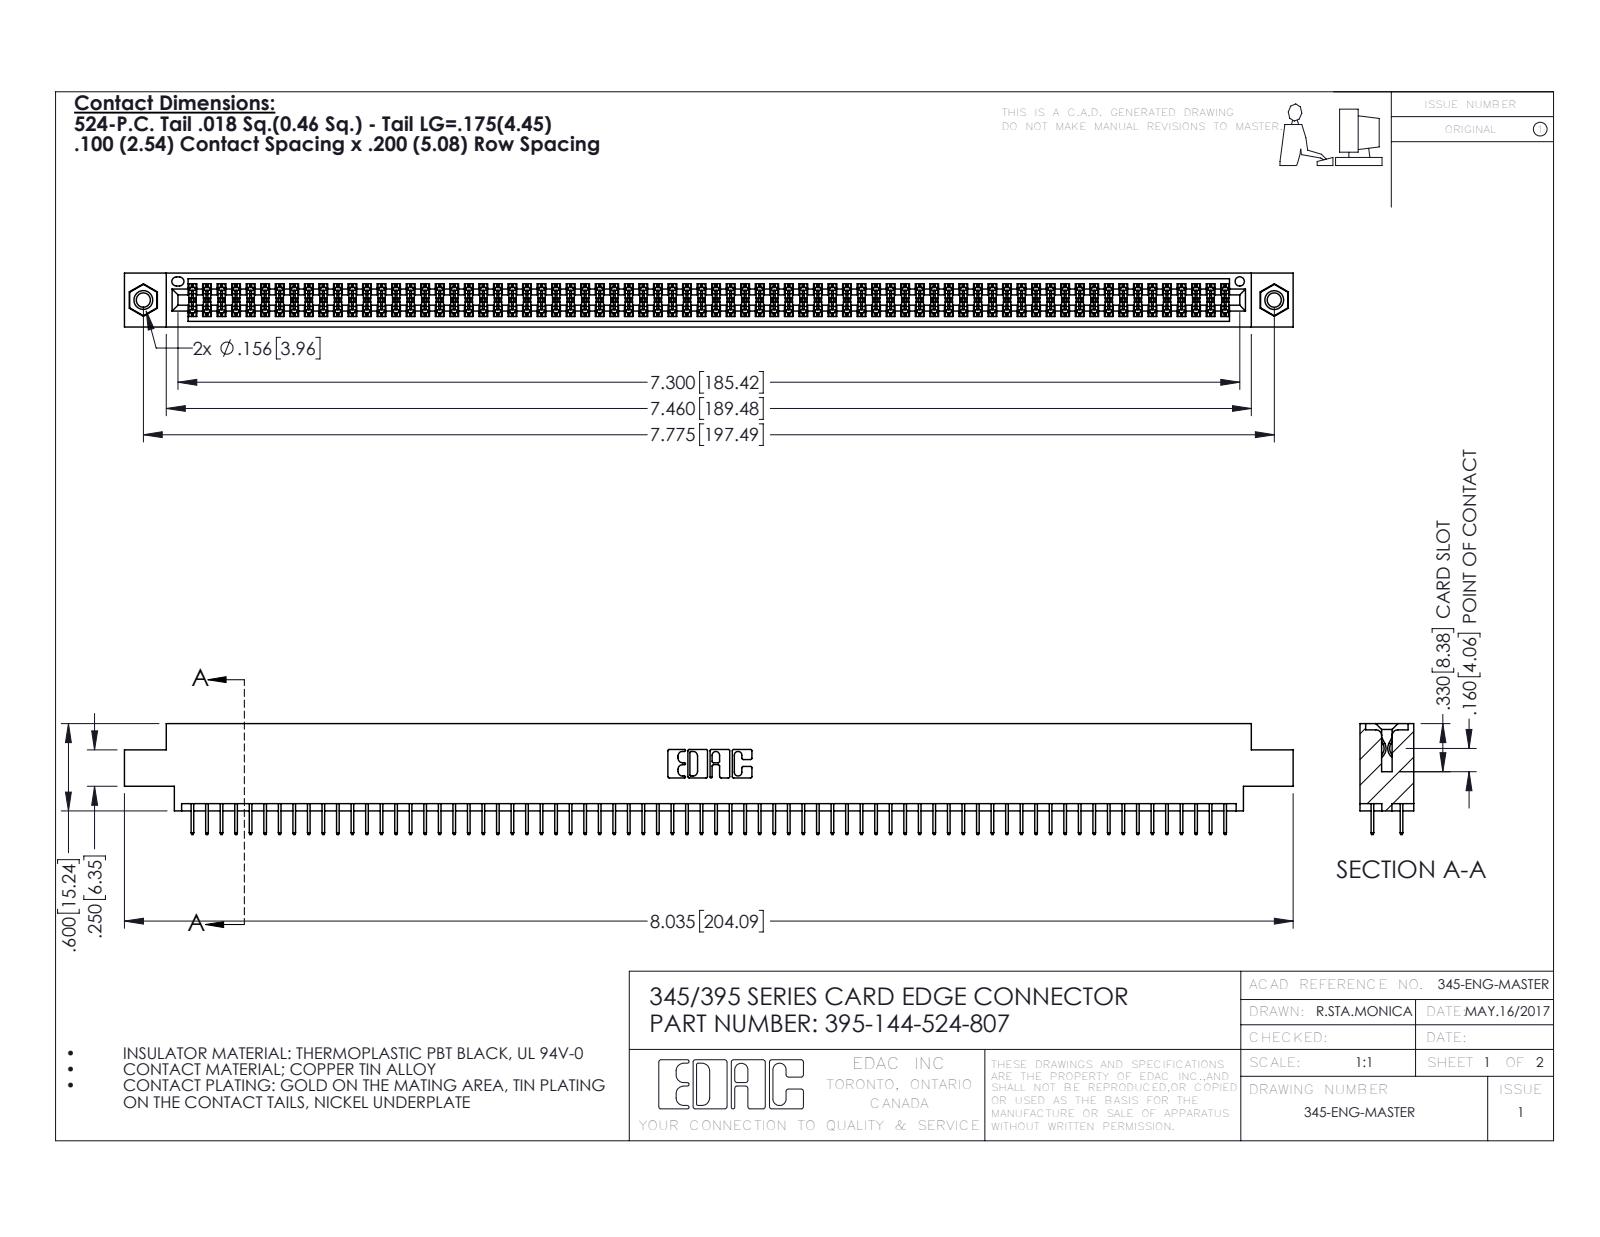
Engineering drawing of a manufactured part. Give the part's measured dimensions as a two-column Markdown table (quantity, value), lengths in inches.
| quantity | value |
| --- | --- |
| part name | 345-292-001_345-293-124; 345 Part_0.170 Offset - 0.156 Dia-TI; 345-250-001_345-250-005-103; 395-144-524-807 |
| STEP written by | SolidWorks 2016 (CONFIG_CONTROL_DESIGN) |
| units | inches |
| bodies | 147 solids, 7966 faces (5732 planar, 2218 cylindrical, 16 other) |
| overall size | 8.035 × 0.762 × 0.37 |
| volume | 1.206 in³ |
| surface area | 45.55 in² |
| round holes (diameter × count) | 0.098 × 2, 0.125 × 2, 0.156 × 2, 0.064 × 1 |
| round bosses / shafts (diameter × count) | 0.155 × 2 |
| partial cylindrical surfaces (radius × count) | 0.006 × 216, 0.01 × 22, 0.007 × 6, 0.031 × 6, 0.026 × 3, 0.014 × 2, 0.019 × 2, 0.022 × 2 |
| main face-to-face distances | 0.072, 0.298, 0.2, 0.37, 0.098, 0.272, 0.025, 0.225, 0.072, 0.175 |
| hole center spacings | 0.27, 7.539, 7.775 |
